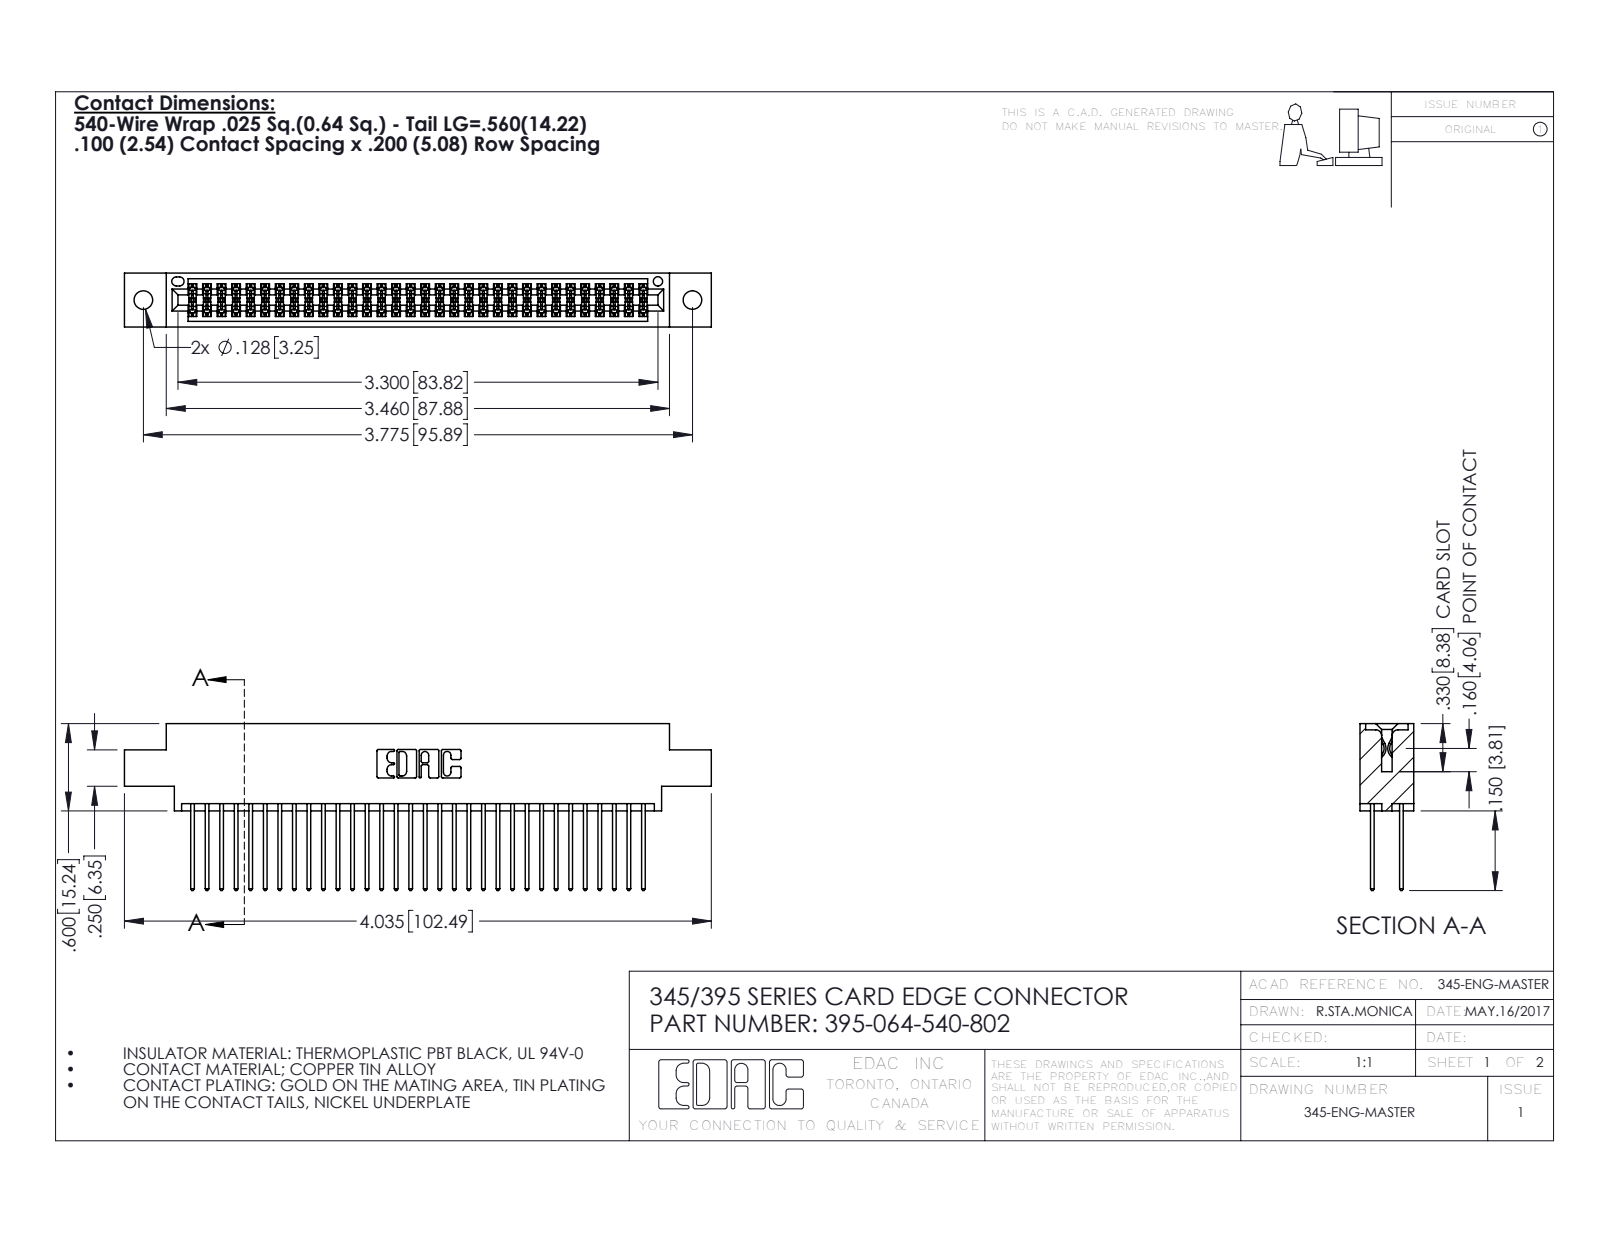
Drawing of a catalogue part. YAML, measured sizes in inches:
part_name: "345 Part_0.170 Offset - 0.128 Dia; 345-292-001_345-293-140; 395-064-540-802"
step_written_by: "SolidWorks 2016 (CONFIG_CONTROL_DESIGN)"
units: inches
bodies: {solids: 65, faces: 3330, planar: 2196, cylindrical: 1134, other: 0}
overall_size: [4.035, 1.147, 0.37]
volume: 0.608
surface_area: 24.05
round_holes:
  - {diameter: 0.128, count: 2}
  - {diameter: 0.064, count: 1}
partial_cylinders:
  - {radius: 0.006, count: 96}
  - {radius: 0.01, count: 64}
  - {radius: 0.01, count: 22}
  - {radius: 0.007, count: 6}
  - {radius: 0.031, count: 6}
  - {radius: 0.026, count: 3}
  - {radius: 0.014, count: 2}
  - {radius: 0.019, count: 2}
face_to_face_distances: [0.298, 0.072, 0.2, 0.098, 0.272, 0.025, 0.37, 0.225, 0.175, 0.149]
hole_center_spacings: [0.27, 3.54, 3.775]
